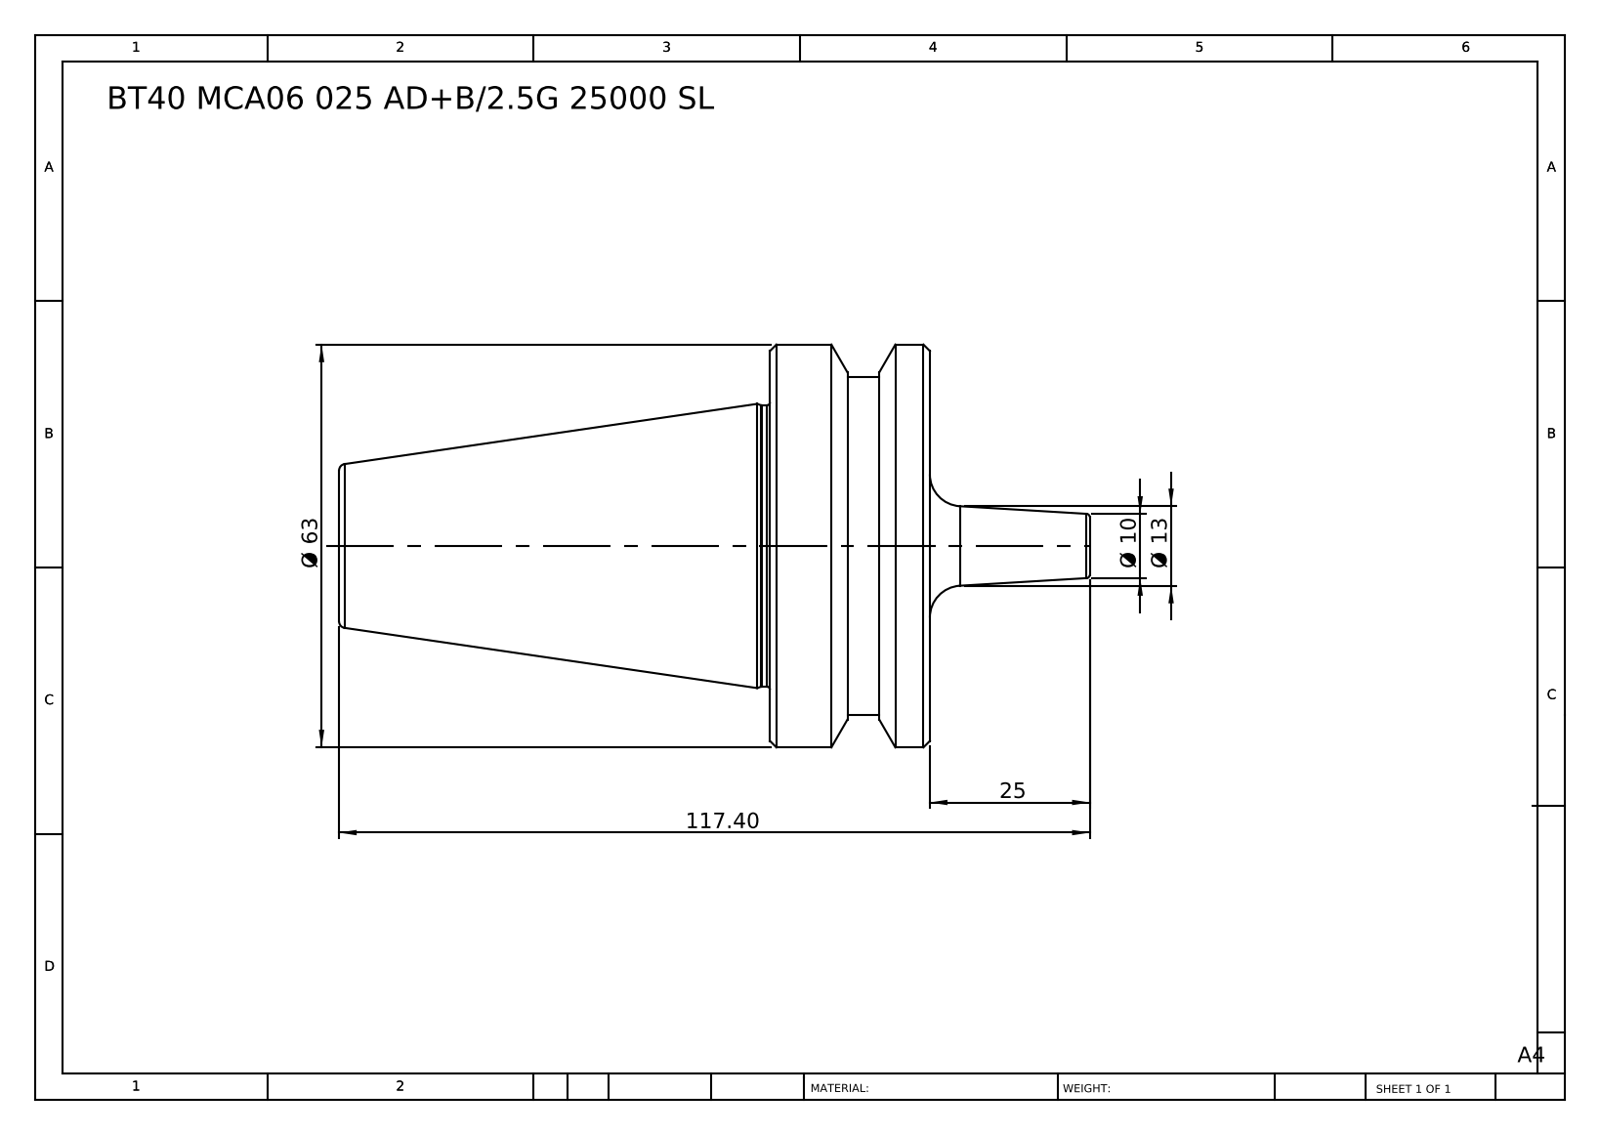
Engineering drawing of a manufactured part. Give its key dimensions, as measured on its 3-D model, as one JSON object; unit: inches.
{"part_name": "BT40 MCA06 025 AD+B-2.5G 25000 SL", "step_written_by": "SolidWorks 2014 (CONFIG_CONTROL_DESIGN)", "units": "inches", "bodies": {"solids": 1, "faces": 38, "planar": 6, "cylindrical": 8, "other": 24}, "overall_size": [4.622, 2.48, 2.48], "volume_in3": 8.615, "surface_area_in2": 29.62, "round_bosses_or_shafts": [[2.48, 1], [2.087, 1], [1.732, 1]], "face_to_face_distances": [0.984, 3.638, 2.654, 0.508, 0.476, 3.13, 0.311, 0.197, 0.673, 3.327]}
